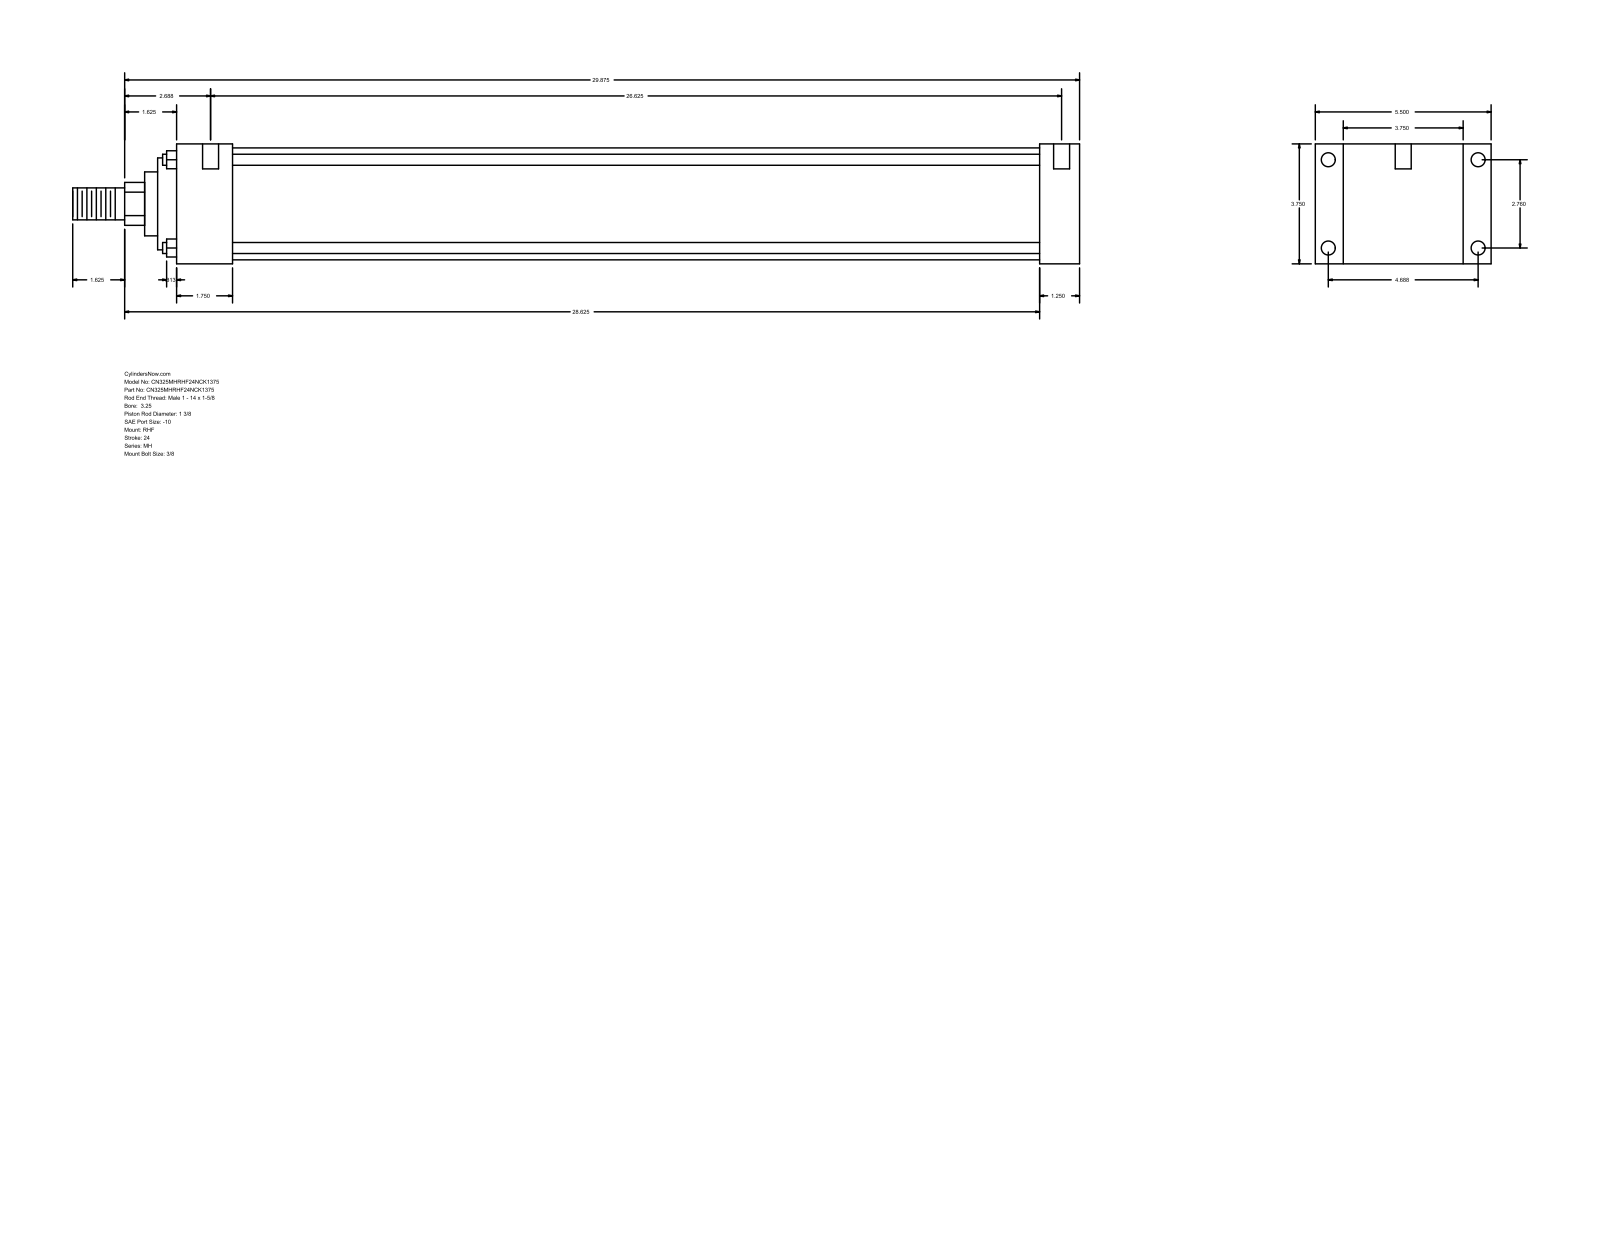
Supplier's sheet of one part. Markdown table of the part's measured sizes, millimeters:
| quantity | value |
| --- | --- |
| part name | MH_RHF__0325_1.375 |
| STEP written by | GSSL Pune (CONFIG_CONTROL_DESIGN) |
| units | millimeters |
| bodies | 0 solids, 90 faces (61 planar, 29 cylindrical, 0 other) |
| overall size | 800.1 × 139.7 × 95.25 |
| round holes (diameter × count) | 5.56 × 4, 11.13 × 4, 12.7 × 2 |
| round bosses / shafts (diameter × count) | 8.76 × 4, 88.9 × 1, 73.03 × 1, 50.8 × 1, 34.92 × 1, 25.4 × 1 |
| partial cylindrical surfaces (radius × count) | 17.06 × 1 |
| main face-to-face distances | 95.24, 31.75, 22.23, 117.47, 685.81, 717.56, 139.7, 44.45, 641.36, 673.11 |
| hole center spacings | 70.1, 119.06, 138.16, 682.63, 1.59, 4.76, 676.28, 677.87 |
